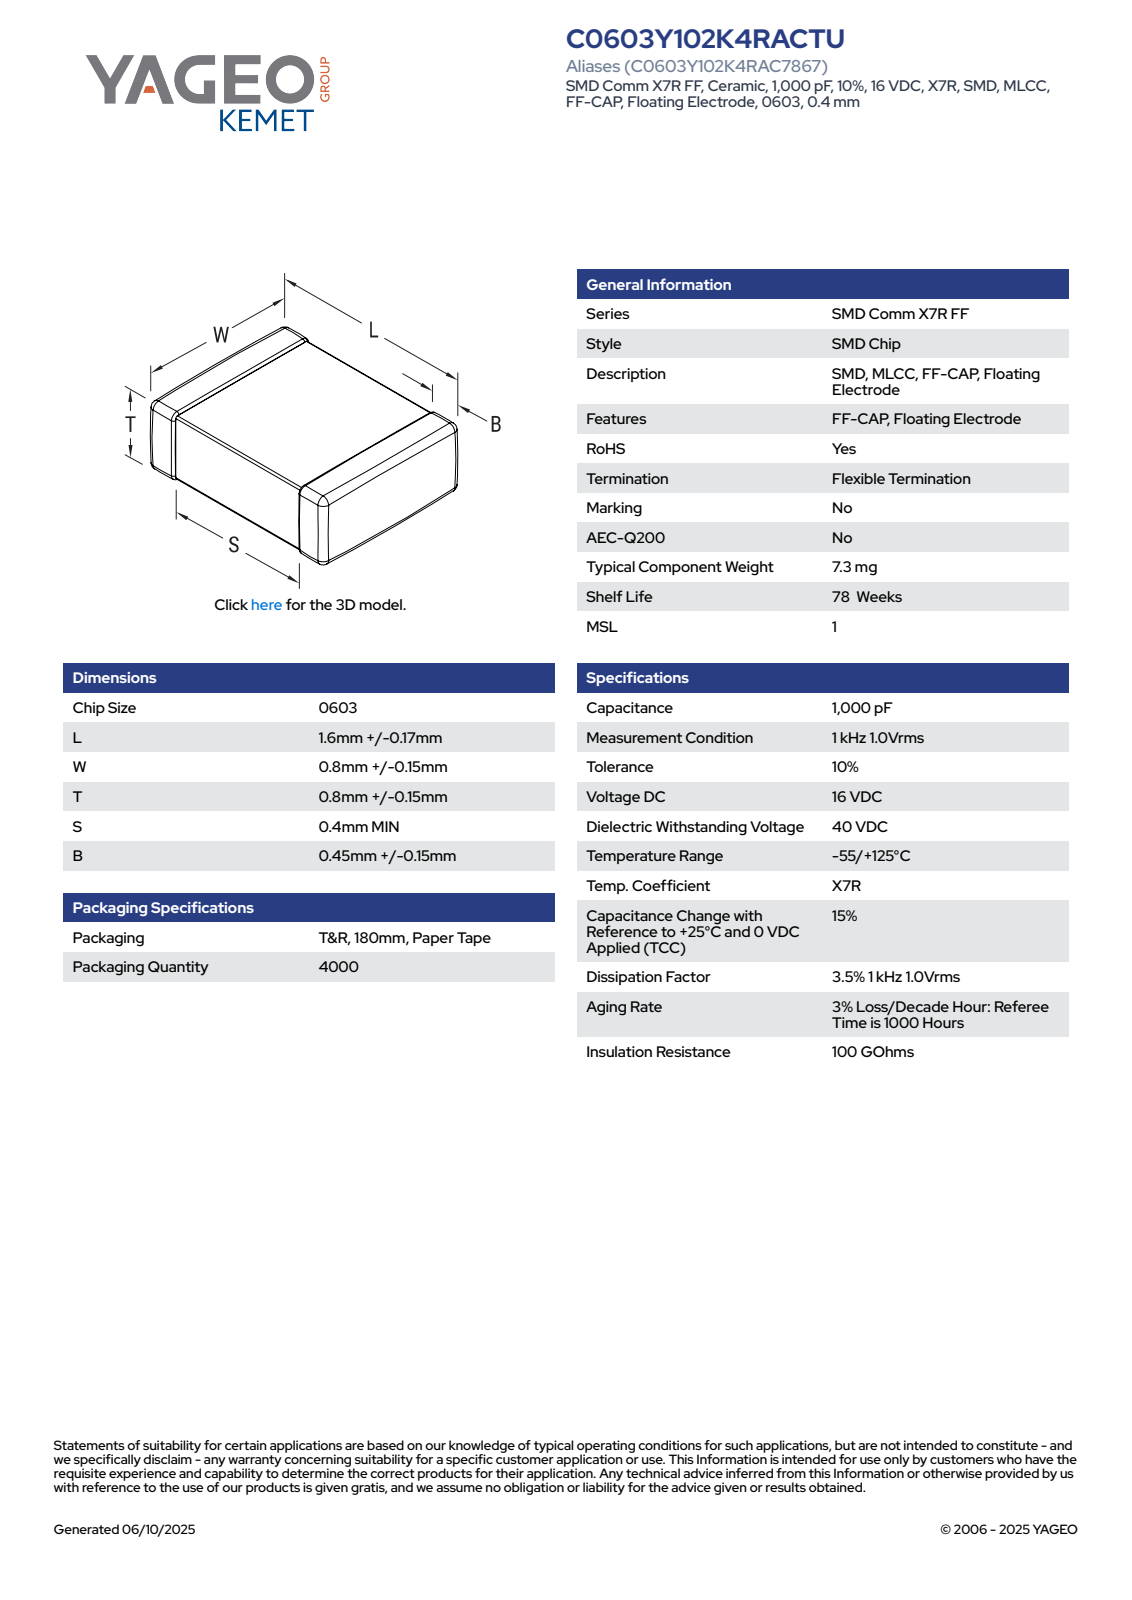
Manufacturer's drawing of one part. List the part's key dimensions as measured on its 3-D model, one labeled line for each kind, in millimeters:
Part name (STEP PRODUCT): CCS_CCSTD_0603_L1.77W0.95T0.95S0.4B0.6
STEP written by: SolidWorks 2021 (AUTOMOTIVE_DESIGN)
Units: millimetres
Bodies: 4 solids, 121 faces (71 planar, 34 cylindrical, 16 other)
Overall size (bounding box): 1.77 × 0.95 × 0.95
Volume: 2 mm³ · Surface area: 9 mm²
Main face-to-face distances: 0.93, 0.95, 0.91, 1.77, 0.94, 0.92, 0.82, 0.96, 0.81, 0.84
